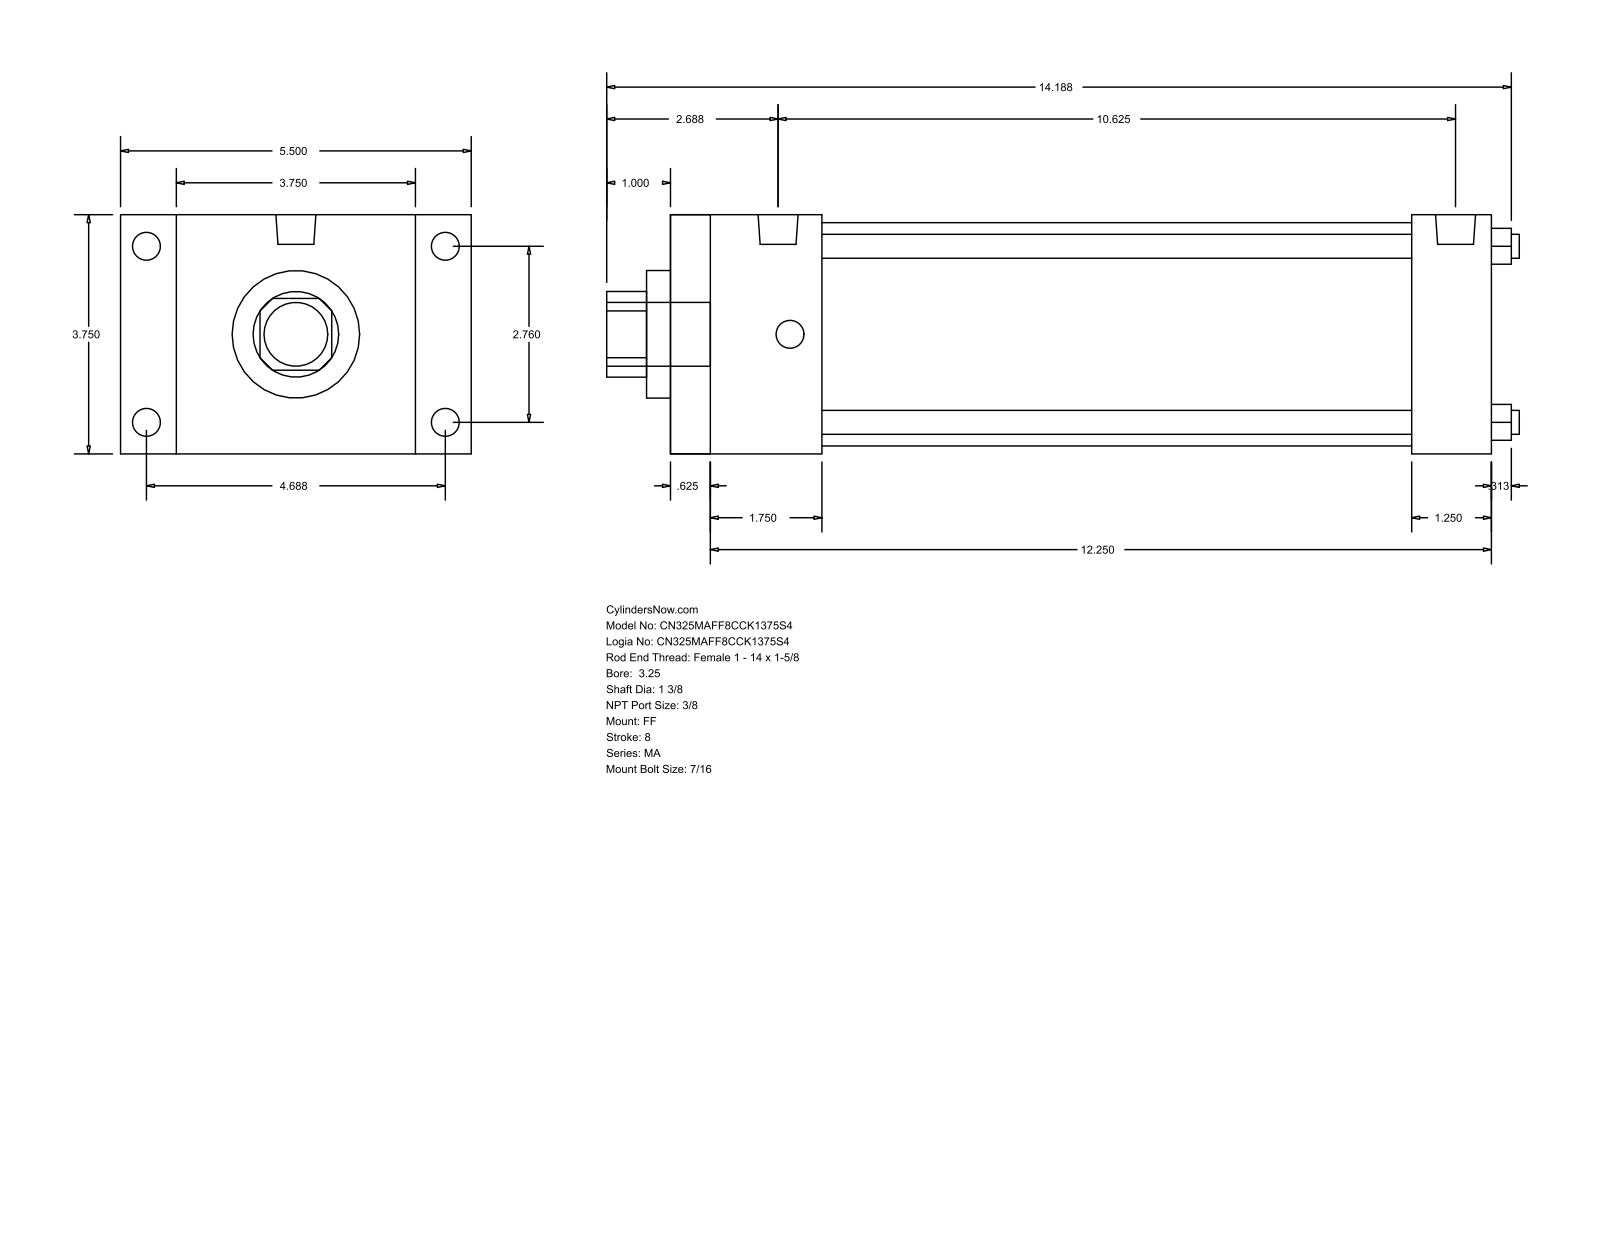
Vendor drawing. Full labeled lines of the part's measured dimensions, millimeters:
Part name (STEP PRODUCT): MA_FF__0325_1.375
STEP written by: GSSL Pune (CONFIG_CONTROL_DESIGN)
Units: millimetres
Bodies: 0 solids, 92 faces (64 planar, 28 cylindrical, 0 other)
Overall size (bounding box): 363.54 × 139.7 × 95.25
Round holes (diameter × count): ⌀9.53 ×4, ⌀34.92 ×1, ⌀50.8 ×1, ⌀88.9 ×1
Round bosses / shafts (diameter × count): ⌀11.11 ×8, ⌀15.93 ×2, ⌀25.4 ×1
Partial cylindrical surfaces — rounded edges, fillets, slot ends (radius × count): R17.06 ×1
Main face-to-face distances: 95.24, 327.03, 15.87, 311.16, 22.23, 117.47, 60.32, 295.28, 44.45, 279.41
Hole centre spacings: 49.57, 70.1, 99.14
